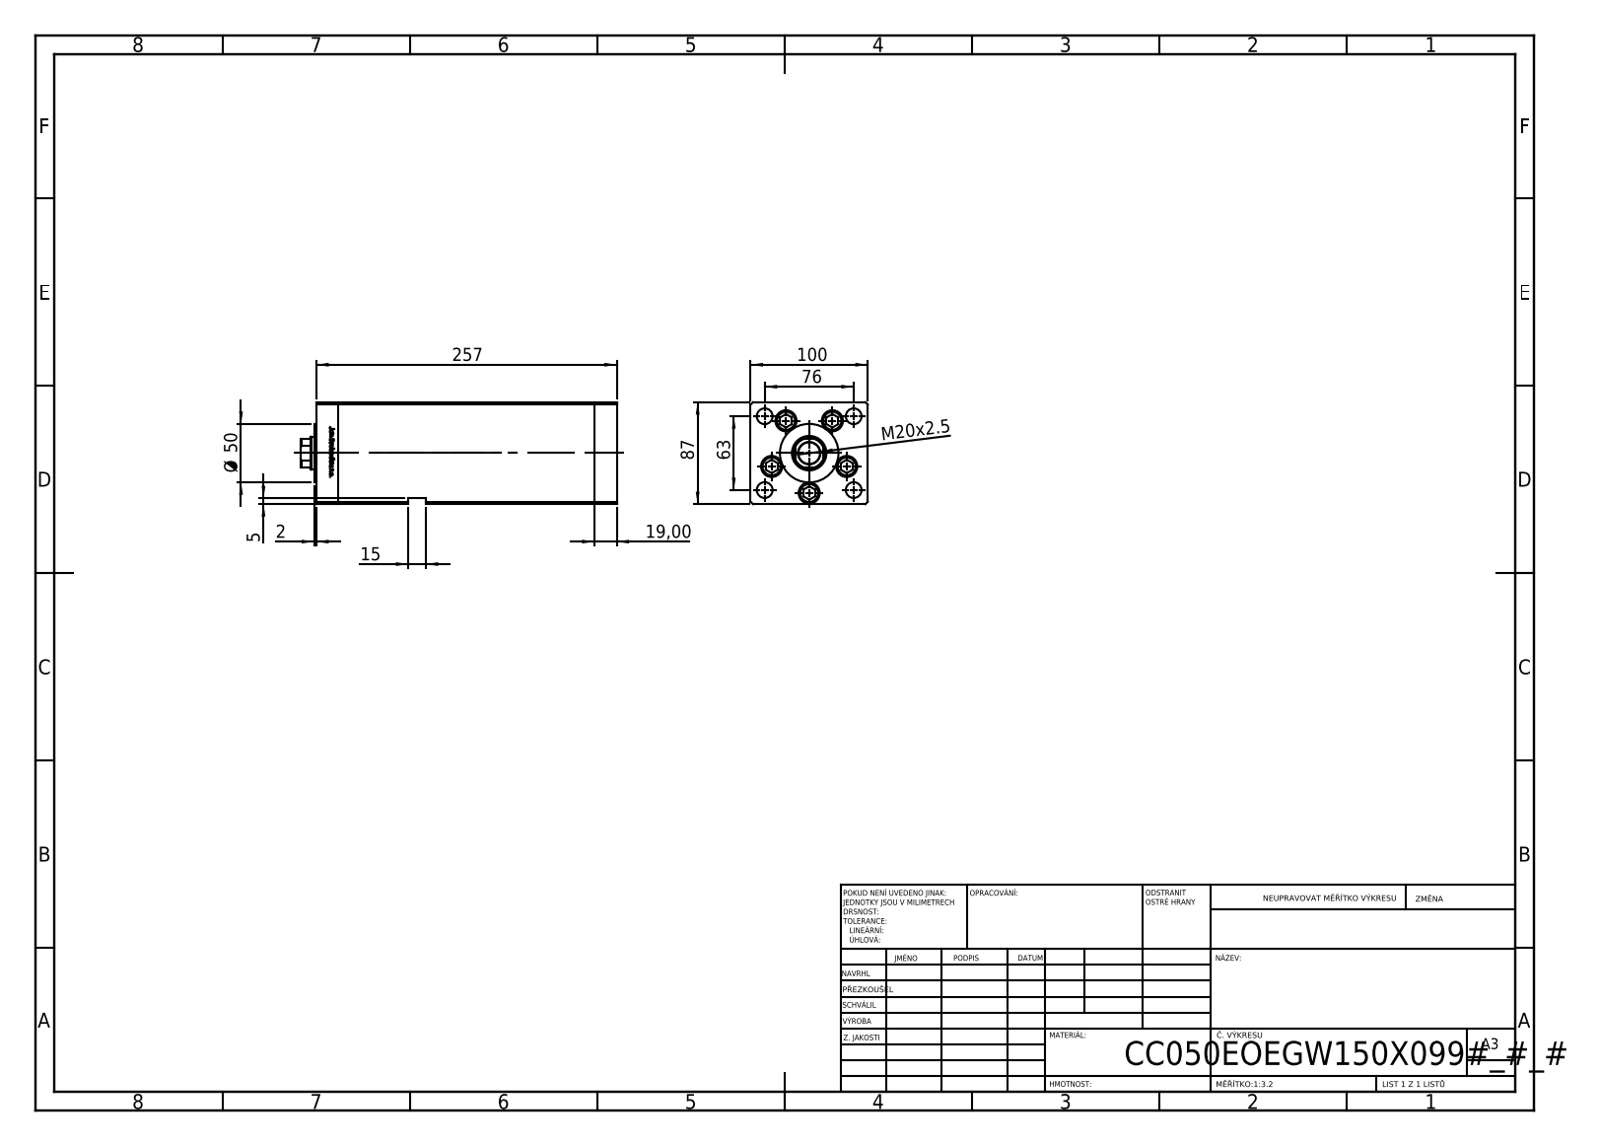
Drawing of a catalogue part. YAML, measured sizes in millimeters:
part_name: "V220C_E MIDDLE; V220C_FRONT_E; V220C_VC_E; V220C BACK_E (+1 more)"
step_written_by: "SolidWorks 2019 (CONFIG_CONTROL_DESIGN)"
units: millimeters
bodies: {solids: 14, faces: 1214, planar: 475, cylindrical: 165, other: 574}
overall_size: [269.5, 100, 87]
volume: 1865000
surface_area: 265778
round_holes:
  - {diameter: 13.5, count: 11}
  - {diameter: 18, count: 5}
  - {diameter: 18.5, count: 5}
  - {diameter: 12.5, count: 4}
  - {diameter: 2, count: 2}
  - {diameter: 13.16, count: 2}
  - {diameter: 28, count: 1}
  - {diameter: 29.5, count: 1}
round_bosses_or_shafts:
  - {diameter: 17, count: 5}
  - {diameter: 8, count: 5}
  - {diameter: 50, count: 1}
partial_cylinders:
  - {radius: 0.93, count: 2}
  - {radius: 13.5, count: 1}
face_to_face_distances: [100, 87, 19, 218.5, 237.5, 34.25, 256.5, 15.25, 203.25, 222.25]
hole_center_spacings: [34, 18.59, 39.64, 49.36, 57.95, 21.03, 38.08, 39.27]
